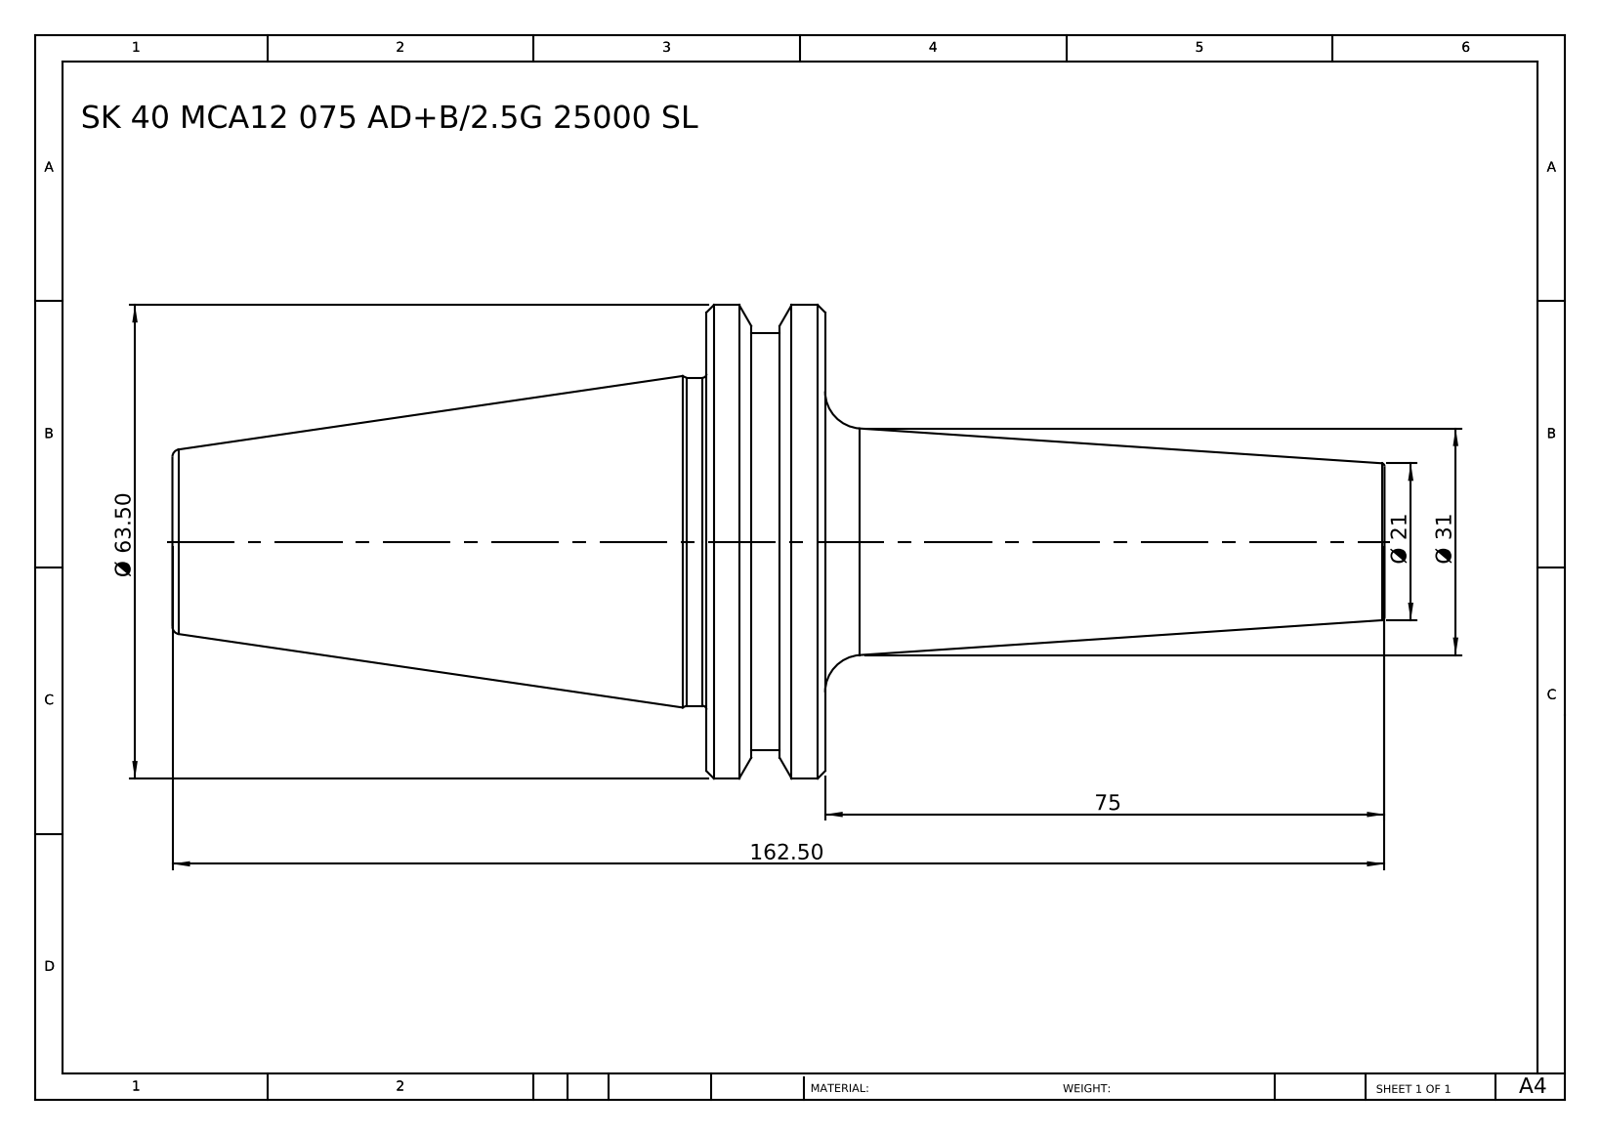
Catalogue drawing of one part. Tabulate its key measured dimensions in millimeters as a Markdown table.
| quantity | value |
| --- | --- |
| part name | SK 40 MCA12 075 AD+B-2.5G 25000 SL |
| STEP written by | SolidWorks 2014 (CONFIG_CONTROL_DESIGN) |
| units | millimeters |
| bodies | 1 solid, 36 faces (6 planar, 8 cylindrical, 22 other) |
| overall size | 162.5 × 63.5 × 63.5 |
| volume | 157 891 mm³ |
| surface area | 22 495 mm² |
| round bosses / shafts (diameter × count) | 63.5 × 1, 56 × 1, 44 × 1 |
| main face-to-face distances | 15.9, 87.5, 71.6, 75, 90.9, 162.5, 81.1, 6.1, 9.8, 81.4 |
